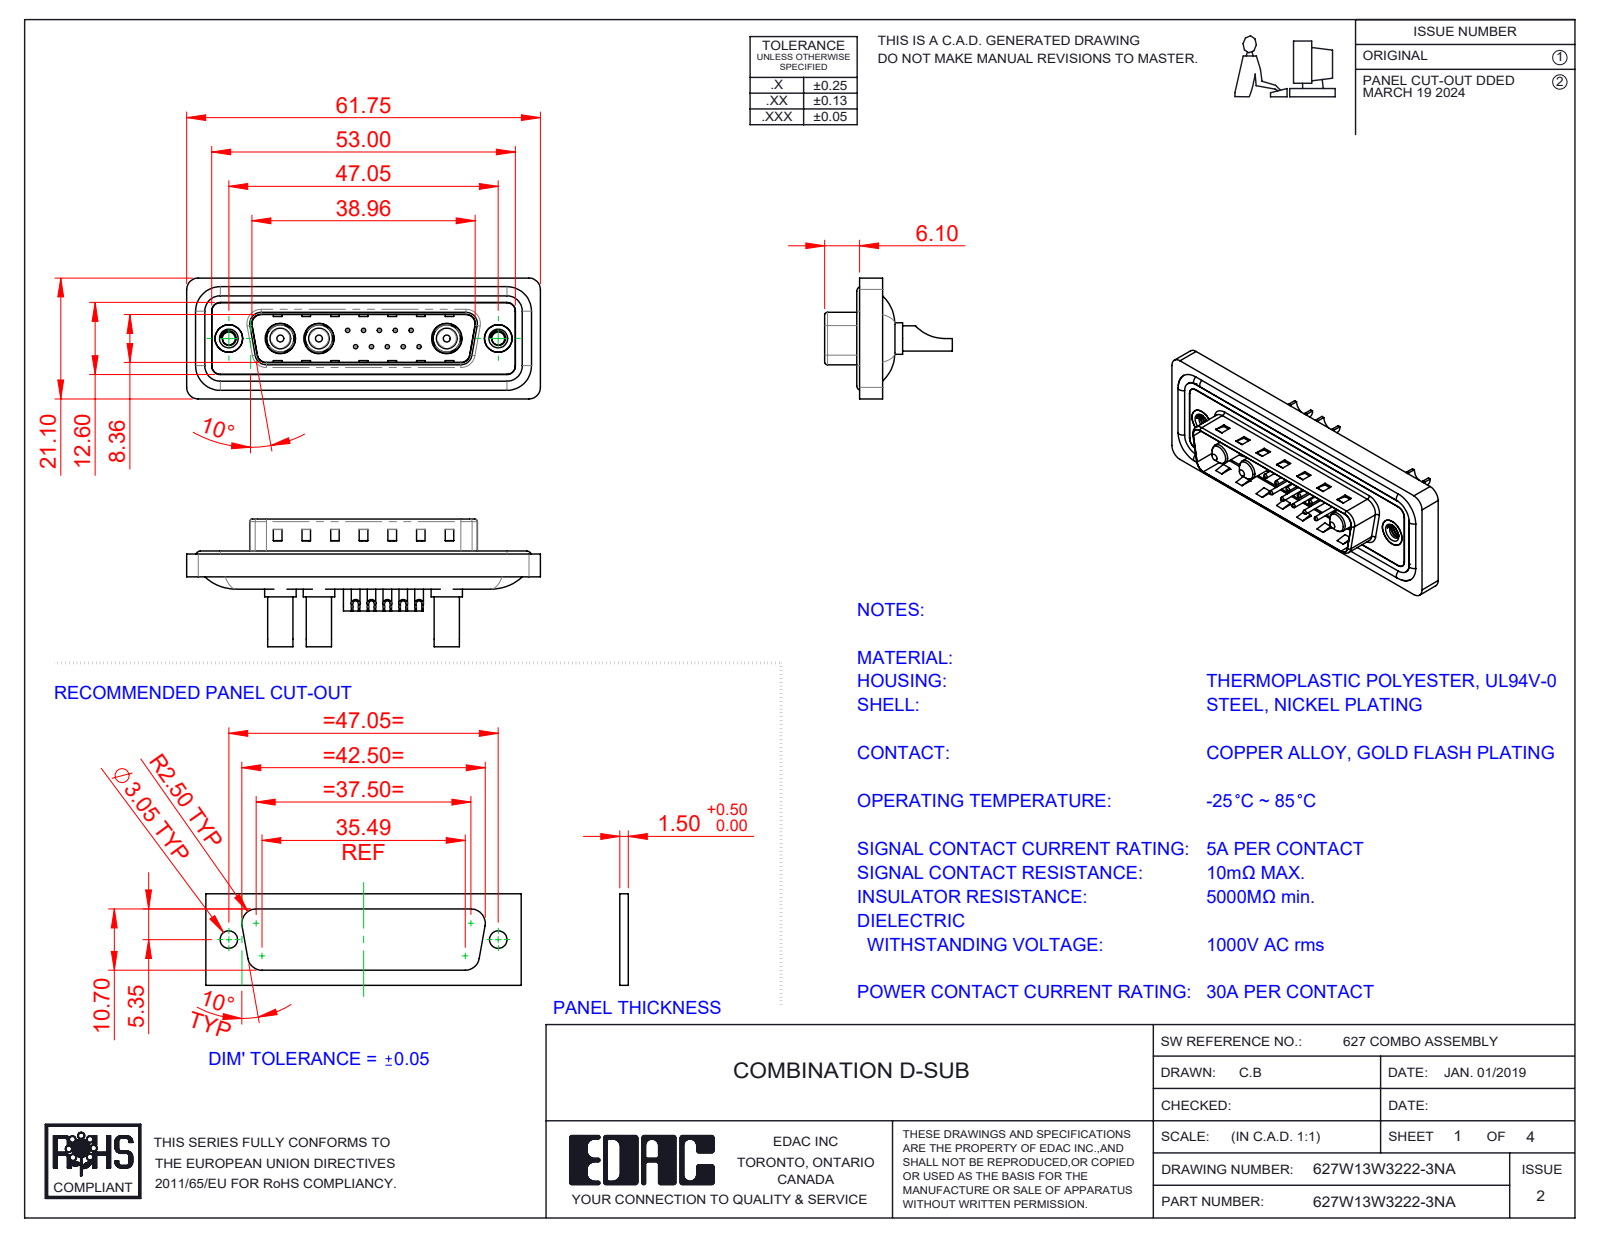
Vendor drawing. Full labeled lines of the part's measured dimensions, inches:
Part name (STEP PRODUCT): 627W13W3222-3NA; 627Combo Contact Row 1_22; 627Combo Shell Rear_25 Contacts; 627Combo Threaded Rivet_A (+5 more)
STEP written by: SolidWorks 2023 (CONFIG_CONTROL_DESIGN)
Units: inches
Bodies: 23 solids, 986 faces (338 planar, 416 cylindrical, 232 other)
Overall size (bounding box): 2.431 × 0.878 × 0.831
Volume: 0.453 in³ · Surface area: 19.03 in²
Round holes (diameter × count): ⌀0.03 ×10, ⌀0.039 ×10, ⌀0.063 ×10, ⌀0.079 ×10, ⌀0.138 ×3, ⌀0.191 ×3, ⌀0.209 ×3, ⌀0.089 ×2, ⌀0.157 ×2, ⌀0.189 ×2, ⌀0.197 ×2
Round bosses / shafts (diameter × count): ⌀0.059 ×10, ⌀0.063 ×4, ⌀0.217 ×3, ⌀0.205 ×3, ⌀0.187 ×3, ⌀0.173 ×3, ⌀0.148 ×3, ⌀0.142 ×3
Partial cylindrical surfaces — rounded edges, fillets, slot ends (radius × count): R0.059 ×22, R0.079 ×18, R0.02 ×8, R0.063 ×8, R0.039 ×6, R0.01 ×4, R0.024 ×4, R0.026 ×4
Main face-to-face distances: 0.016, 0.059, 0.043, 0.063, 0.02, 0.122, 0.114, 0.032, 0.377, 0.161
Hole centre spacings: 0.124, 0.109, 0.198, 0.218, 0.295, 0.198, 0.327, 0.398
